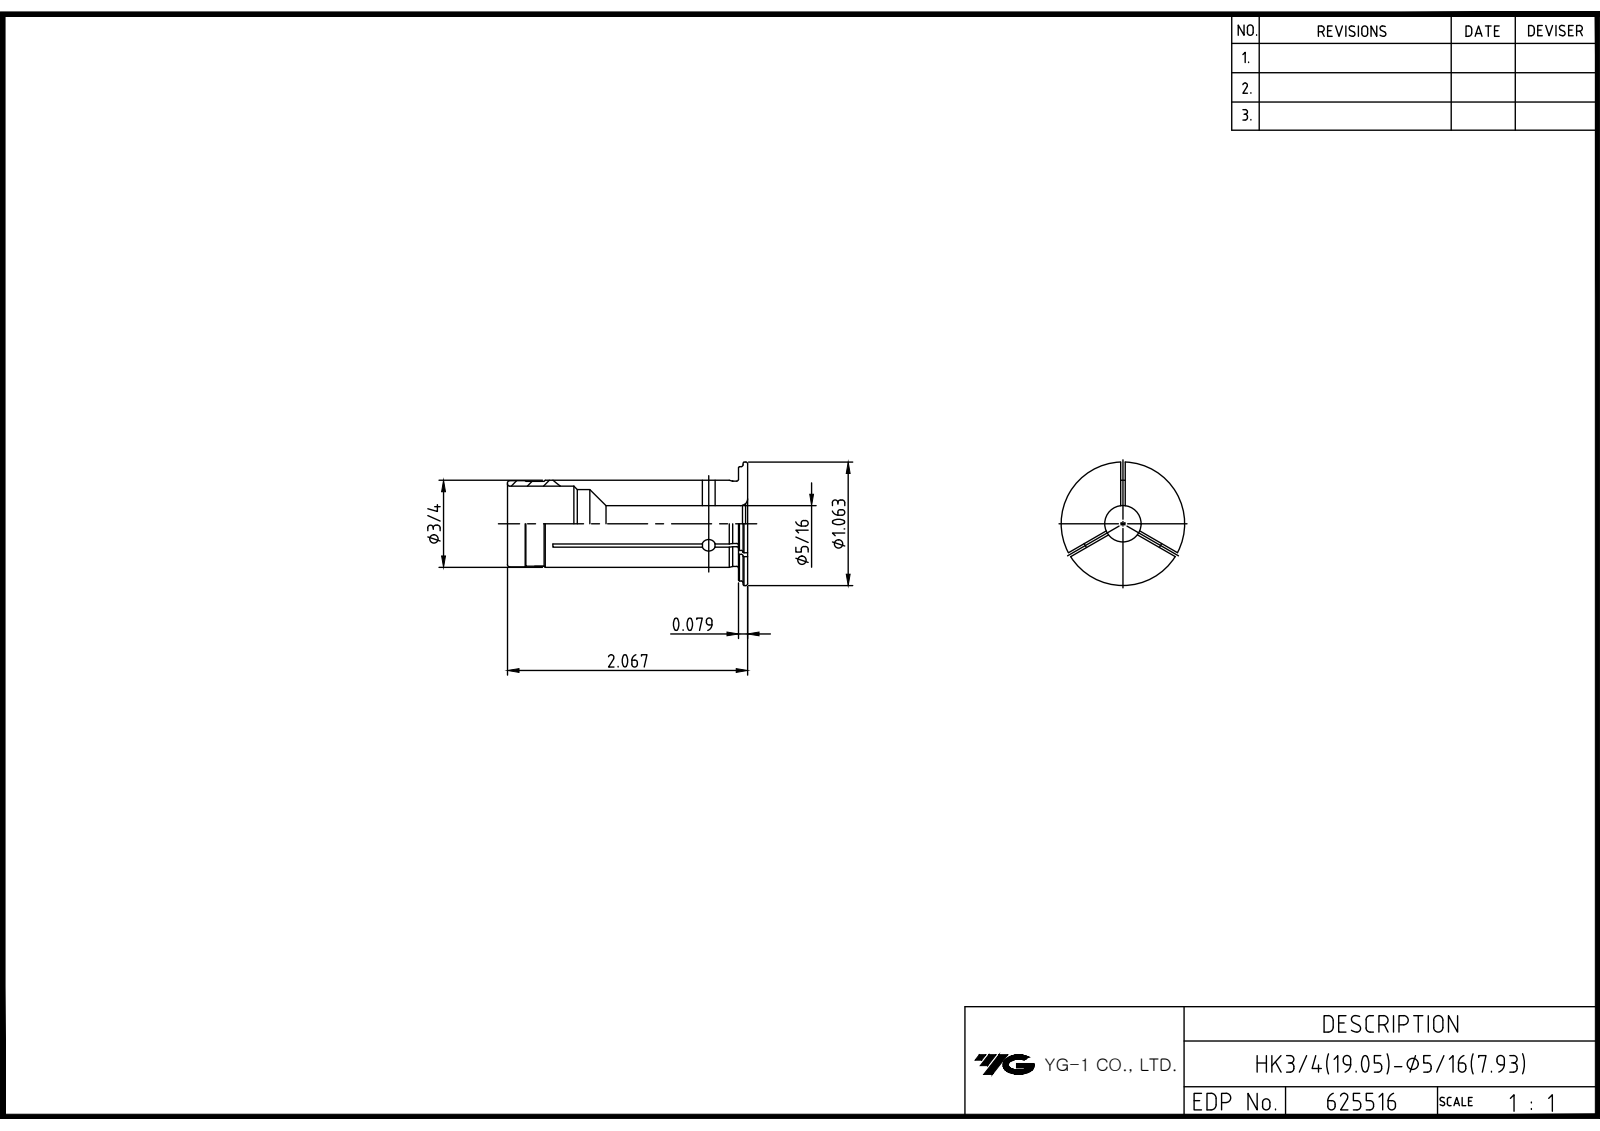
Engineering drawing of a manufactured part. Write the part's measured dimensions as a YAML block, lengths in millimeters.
part_name: "LO-HK19.05-7.9375"
step_written_by: "Autodesk Inventor 2022 (AUTOMOTIVE_DESIGN)"
units: millimeters
bodies: {solids: 1, faces: 12, planar: 4, cylindrical: 6, other: 2}
overall_size: [52.5, 27, 27]
volume: 9816
surface_area: 5953
round_holes:
  - {diameter: 7.94, count: 1}
  - {diameter: 15, count: 1}
  - {diameter: 16.5, count: 1}
round_bosses_or_shafts:
  - {diameter: 27, count: 1}
  - {diameter: 25, count: 1}
  - {diameter: 19.05, count: 1}
face_to_face_distances: [2, 1, 50.5, 51.5, 52.5]
